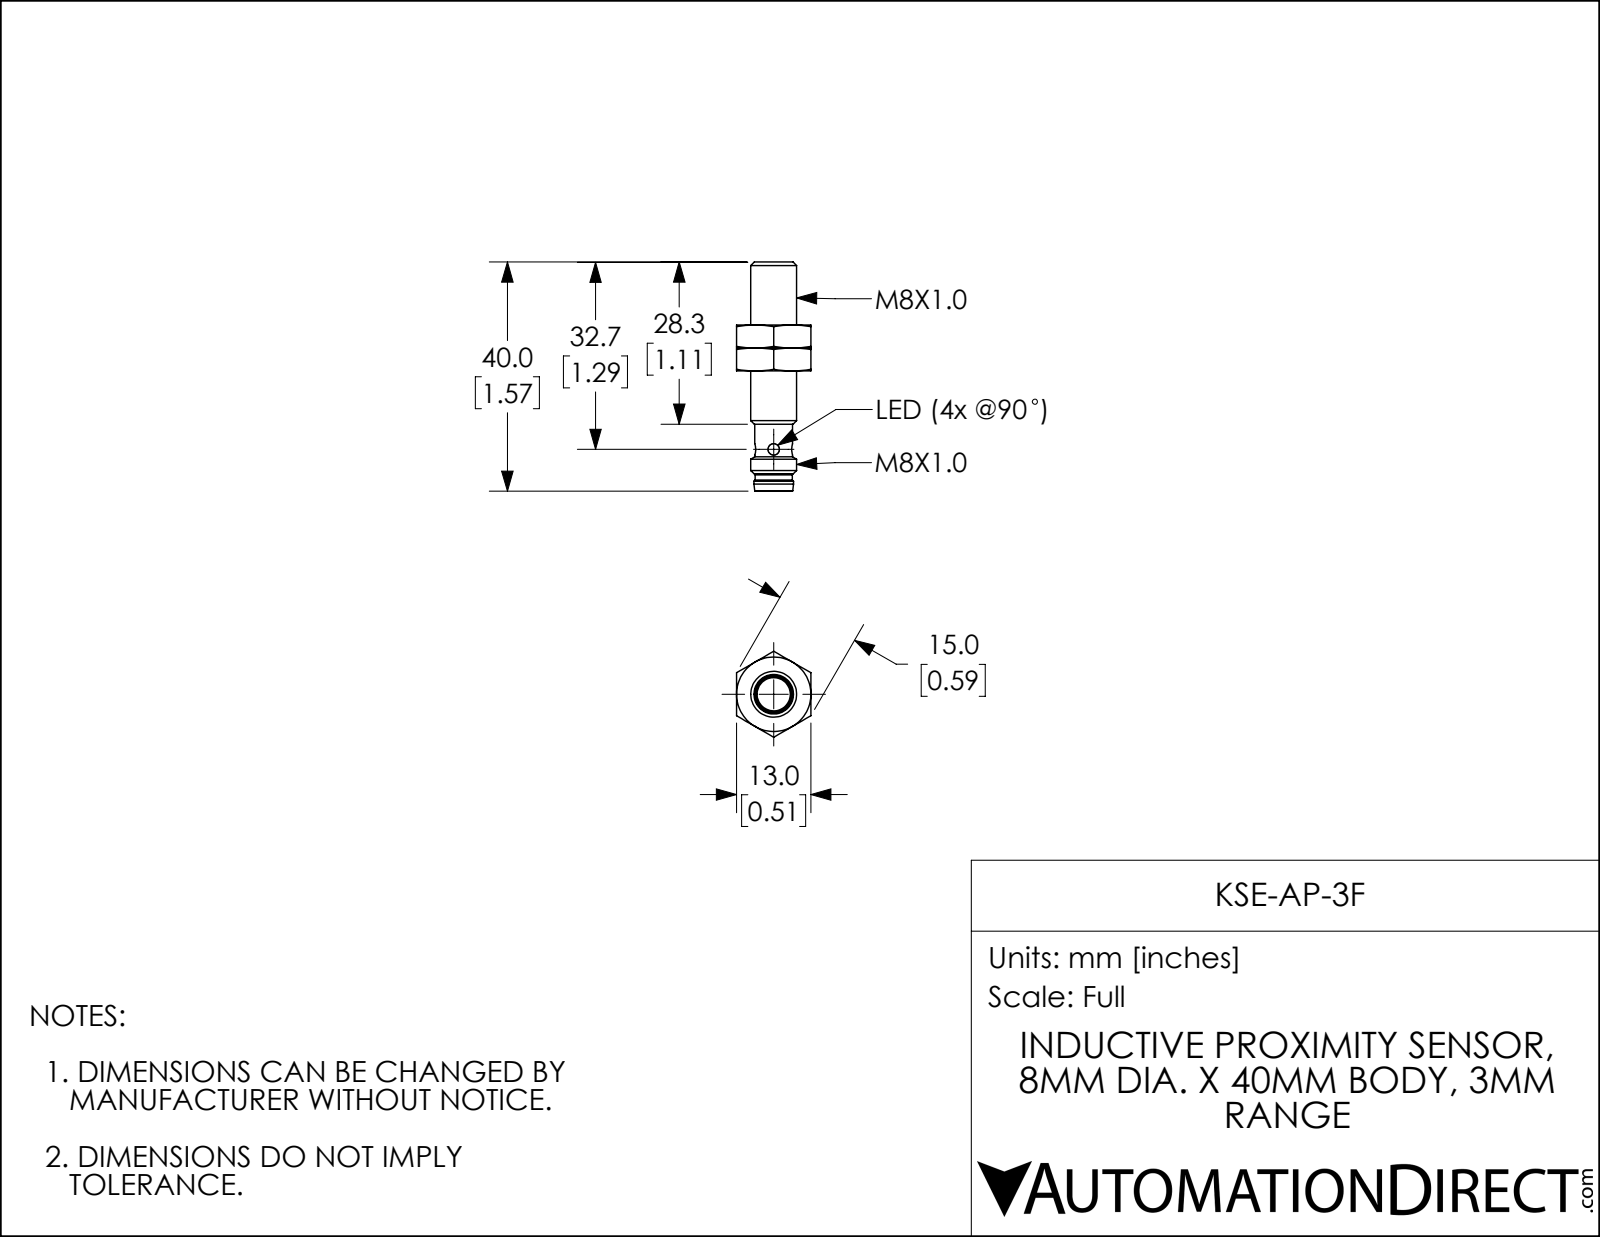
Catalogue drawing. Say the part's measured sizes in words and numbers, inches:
The part is named "KSE-AP-3F". Its 3-D file was written by "SolidWorks 2017 (AUTOMOTIVE_DESIGN)". It is 3 solids with 77 faces: 22 planar, 14 cylindrical and 41 other. Overall it measures 1.575 by 0.591 by 0.512 inches. Its volume is 0.157 cubic inches and its surface area 3.25 square inches. Round holes: 1 of diameter 0.228, 1 of diameter 0.254, 1 of diameter 0.272. Round bosses or shafts: 1 of diameter 0.315, 1 of diameter 0.272, 1 of diameter 0.26, 1 of diameter 0.256, 1 of diameter 0.25. Partial cylindrical surfaces (rounded edges, fillets, slot ends): 4 of radius 0.13. The main face-to-face distances are 0.512, 0.157, 0.315, 0.746, 0.589, 0.431, 0.628, 0.785, 0.943, 1.374.
